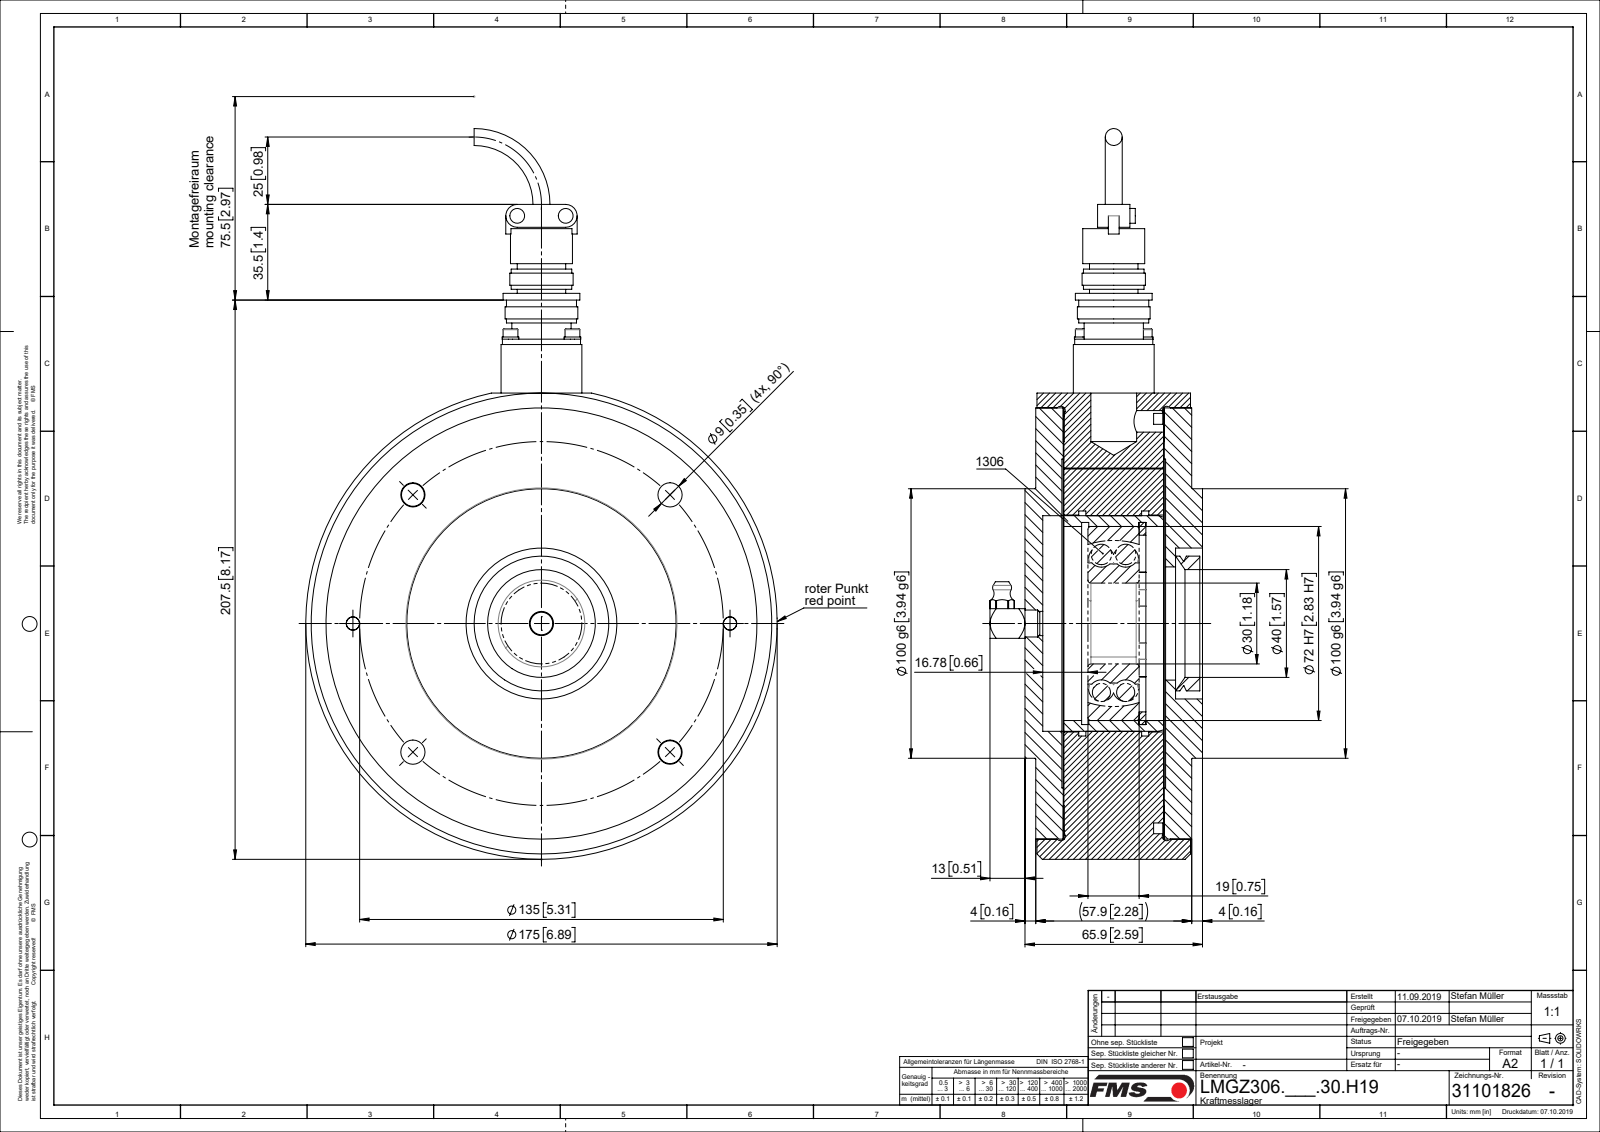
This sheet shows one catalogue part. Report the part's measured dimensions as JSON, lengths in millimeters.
{"part_name": "ZEICHNUNG8; ZEICHNUNG7; L50324_STP; L4974404 (+8 more)", "step_written_by": "Mechanical Desktop 2009 (CONFIG_CONTROL_DESIGN)", "units": "millimeters", "bodies": {"solids": 23, "faces": 437, "planar": 116, "cylindrical": 247, "other": 74}, "overall_size": [271.15, 175, 80.4], "volume_mm3": 1287000, "surface_area_mm2": 272723, "round_holes": [[9, 5], [2.6, 4], [3.2, 4], [3.4, 4], [5, 2], [6.6, 2], [8, 2], [8.5, 2], [11, 2], [10, 1], [17, 1], [23, 1]], "round_bosses_or_shafts": [[5.5, 6], [6.2, 4], [3, 4], [2.5, 4], [10, 3], [6, 2], [175, 1], [160, 1]], "partial_cylinders_radius": [[4.25, 2], [7.5, 2]], "face_to_face_distances": [37.25, 10.2, 10.45, 47.45, 47.7, 38, 37, 0.5, 9.7, 48.2], "hole_center_spacings": [16.26, 23, 48.72, 52.67, 67.5, 95.46, 115.55, 127.04]}
